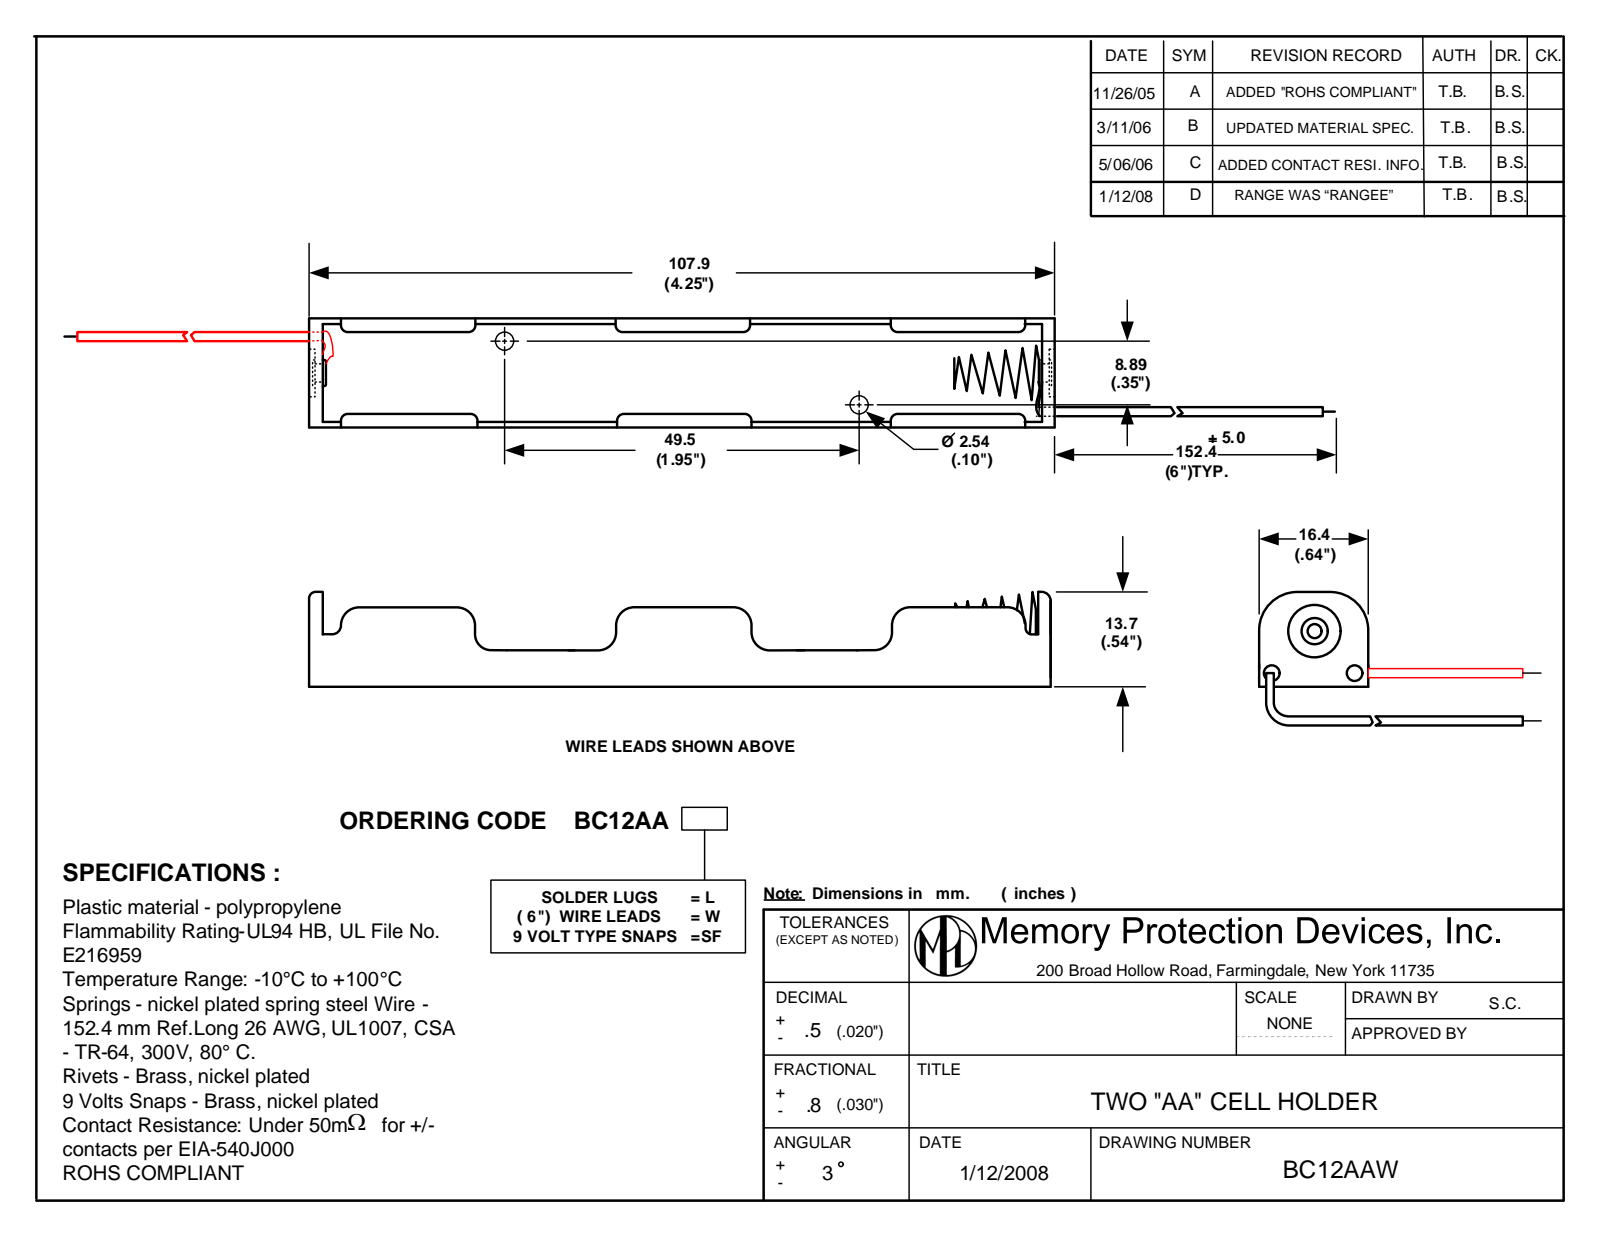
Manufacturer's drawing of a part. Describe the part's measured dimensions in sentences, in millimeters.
The part is named "BC12AAW". Its 3-D file was written by "SolidWorks 2016 (AUTOMOTIVE_DESIGN)". It is 7 solids with 279 faces: 77 planar, 124 cylindrical and 78 other. Overall it measures 417.8 by 16.2 by 13.7 millimeters. Its volume is 4 738 cubic millimeters and its surface area 10 432 square millimeters. Round holes: 4 of diameter 2.5, 2 of diameter 2.54, 1 of diameter 0.4, 1 of diameter 2.3, 1 of diameter 3, 1 of diameter 8. Round bosses or shafts: 1 of diameter 6.2, 1 of diameter 5, 1 of diameter 0.81. Partial cylindrical surfaces (rounded edges, fillets, slot ends): 28 of radius 0.3, 12 of radius 1.91, 2 of radius 3.57, 2 of radius 4.5, 2 of radius 4.73, 1 of radius 0.32. The main face-to-face distances are 1.3, 14.9, 0.65, 16.2, 13.6, 2.55, 105.25, 102.7, 107.8, 0.31. The hole center spacings are 8.6, 9.5, 49.7, 50.6, 11.06.
